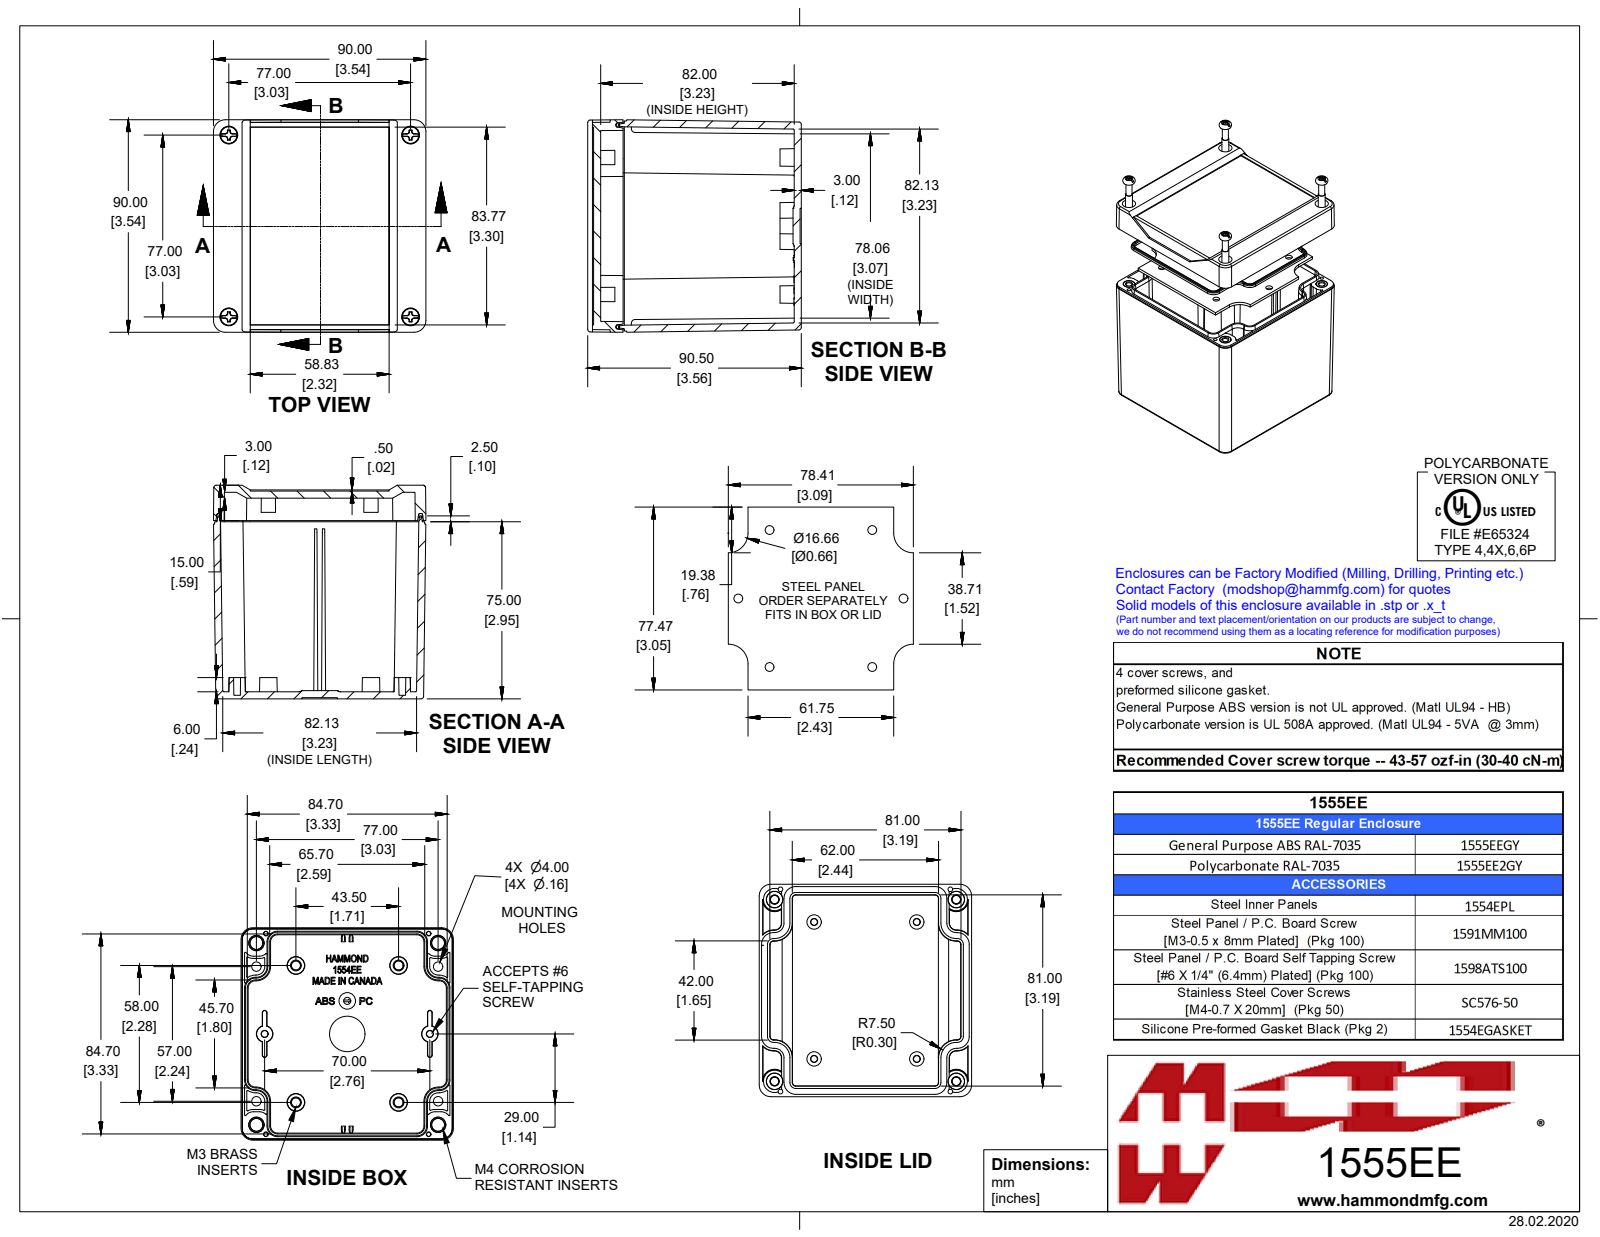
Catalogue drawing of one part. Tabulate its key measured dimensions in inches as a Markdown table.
| quantity | value |
| --- | --- |
| part name | 1555EE2GY |
| STEP written by | SolidWorks 2019 (AUTOMOTIVE_DESIGN) |
| units | inches |
| bodies | 15 solids, 1807 faces (709 planar, 316 cylindrical, 782 other) |
| overall size | 3.563 × 3.543 × 3.543 |
| volume | 9.969 in³ |
| surface area | 185.6 in² |
| round holes (diameter × count) | 0.276 × 5, 0.079 × 4, 0.097 × 4, 0.128 × 4, 0.138 × 4, 0.591 × 1 |
| round bosses / shafts (diameter × count) | 0.25 × 4, 0.218 × 4, 0.21 × 4, 0.19 × 4, 0.154 × 4, 0.153 × 4, 0.15 × 4, 0.135 × 4 |
| partial cylindrical surfaces (radius × count) | 0.02 × 24, 0.039 × 8, 0.197 × 8, 0.187 × 4, 0.059 × 2 |
| main face-to-face distances | 0.118, 3.346, 0.059, 3.465, 3.228, 0.374, 0.492, 0.433, 0.098, 0.02 |
| hole center spacings | 0.197, 0.758, 0.782, 1.427, 2.144, 2.203, 2.338, 2.401 |
